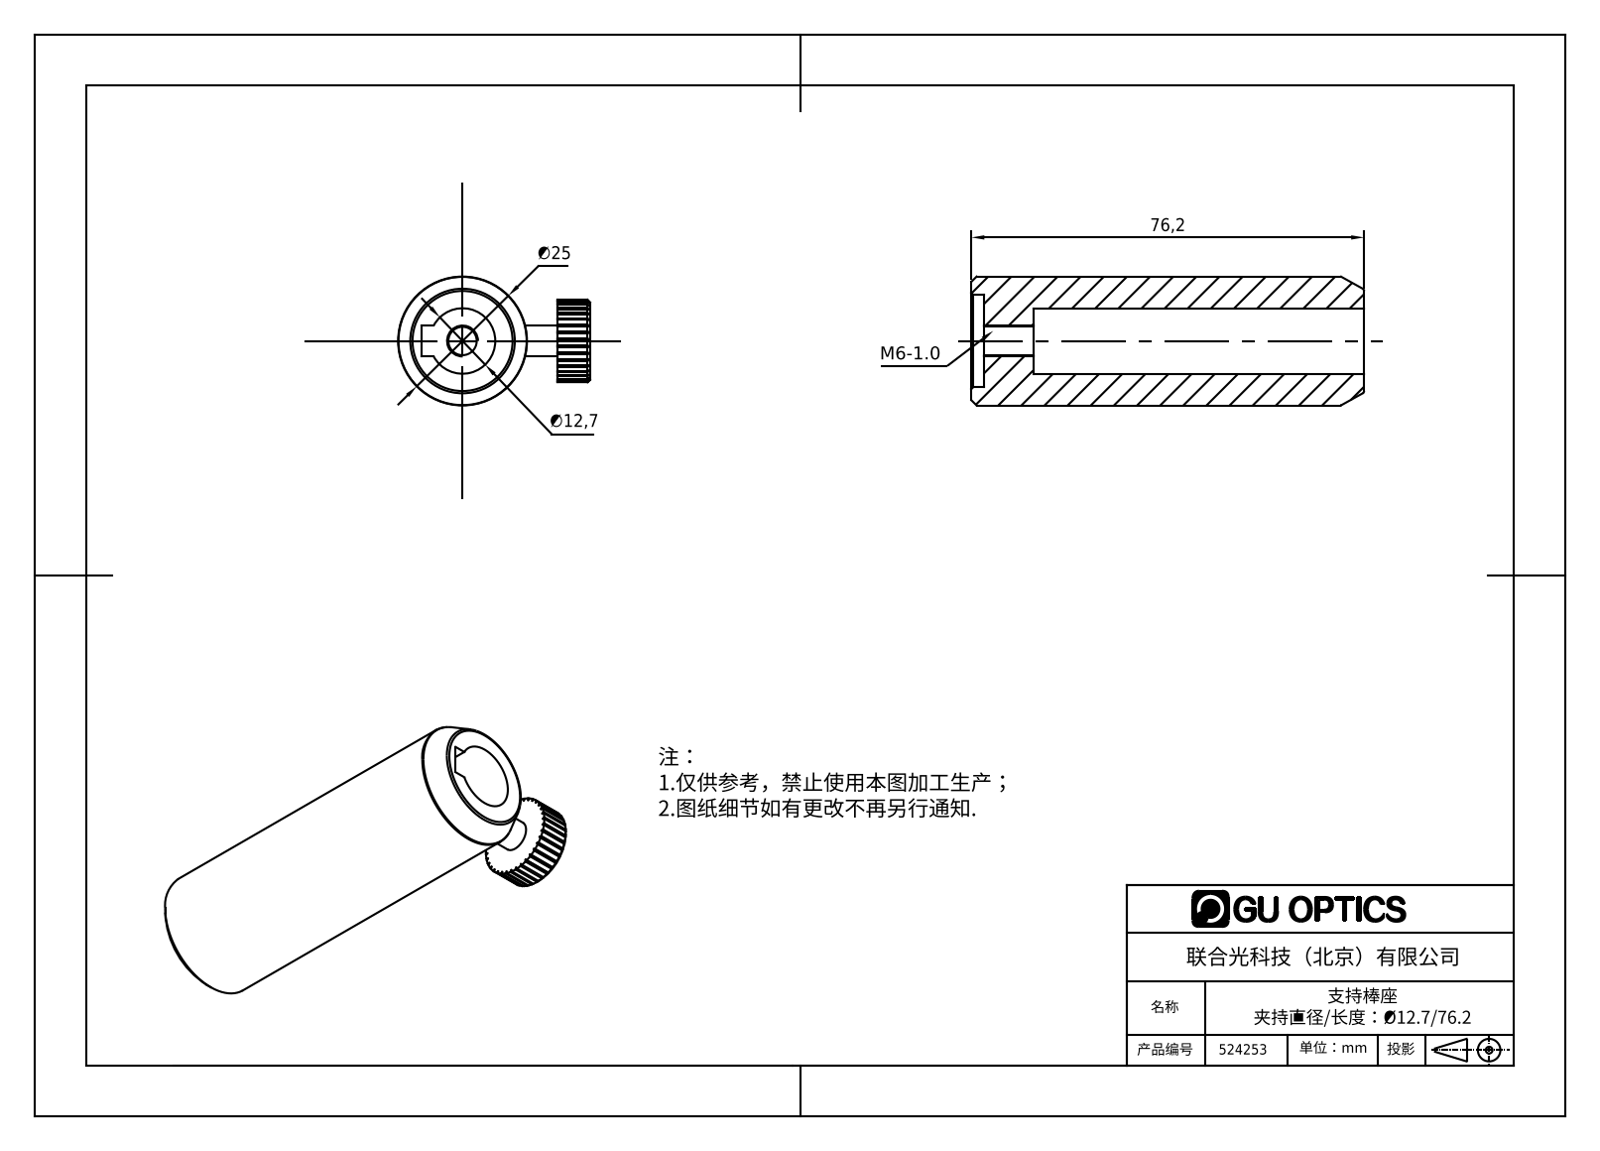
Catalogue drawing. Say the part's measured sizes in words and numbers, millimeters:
The part is named "PH-3". Its 3-D file was written by "SolidWorks 2012 (CONFIG_CONTROL_DESIGN)". It is 0 solids with 145 faces: 94 planar, 43 cylindrical and 8 other. Overall it measures 76.2 by 37.25 by 25 millimeters. Round holes: 2 of diameter 6, 1 of diameter 12.7, 1 of diameter 18. Round bosses or shafts: 1 of diameter 25, 1 of diameter 3. Partial cylindrical surfaces (rounded edges, fillets, slot ends): 1 of radius 8. The main face-to-face distances are 26.35, 75.7, 32.75, 6.4, 6, 0.5, 76.2, 7.65, 5, 14.35.
